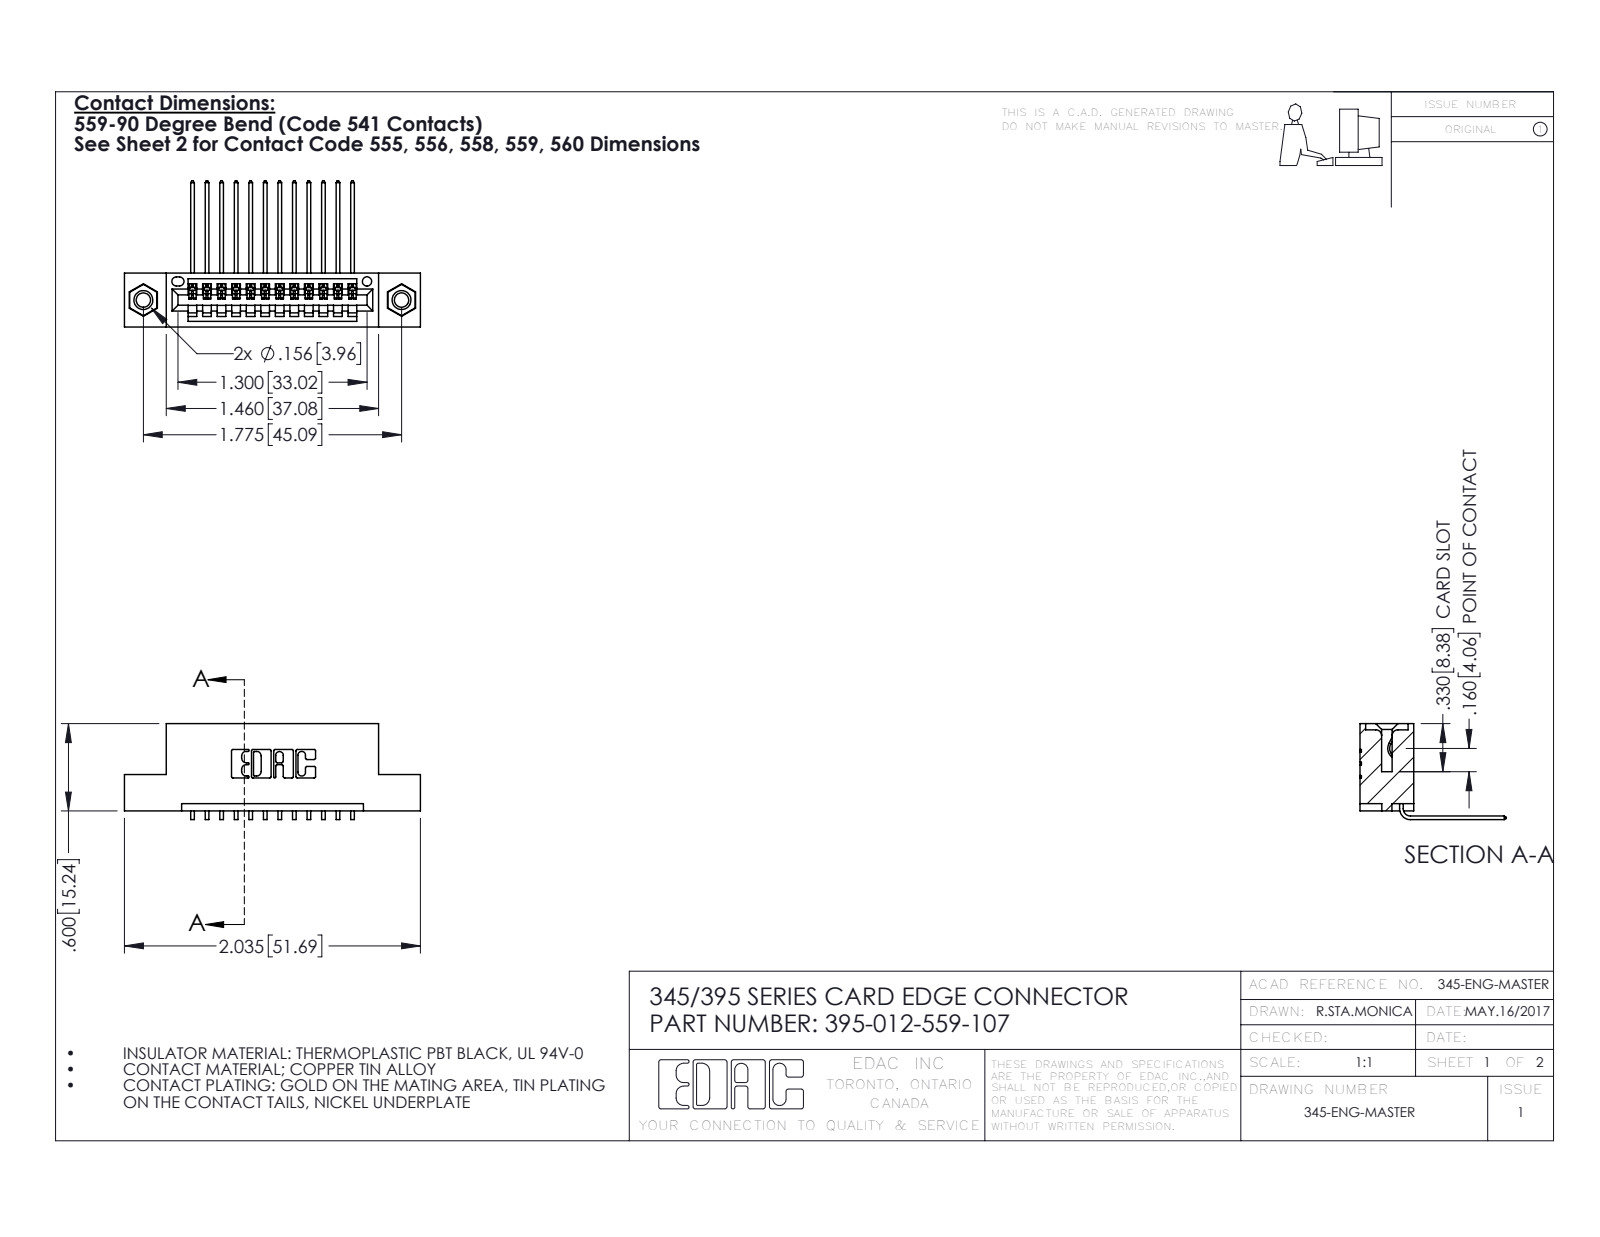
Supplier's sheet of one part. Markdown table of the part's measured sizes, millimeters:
| quantity | value |
| --- | --- |
| part name | 345-250-001_345-250-005-103; 395-012-559-107; 345-292-001_558 559 Tail - 1; 345 Part_Flush Mounting Lugs - 0.156 Dia-TI |
| STEP written by | SolidWorks 2016 (CONFIG_CONTROL_DESIGN) |
| units | millimeters |
| bodies | 15 solids, 906 faces (616 planar, 274 cylindrical, 16 other) |
| overall size | 51.7 × 25.5 × 16.7 |
| volume | 4 690 mm³ |
| surface area | 6 093 mm² |
| round holes (diameter × count) | 2.5 × 2, 3.2 × 2, 4 × 2, 1.6 × 1 |
| round bosses / shafts (diameter × count) | 3.9 × 2 |
| partial cylindrical surfaces (radius × count) | 0.2 × 24, 0.3 × 22, 0.2 × 6, 0.8 × 6, 0.7 × 3, 0.8 × 2, 1 × 2, 0.4 × 1 |
| main face-to-face distances | 5.1, 1.8, 7.6, 9.4, 2.5, 6.9, 0.6, 2.5, 15.2, 7.6 |
| hole center spacings | 6.9, 39.2, 45.1 |
